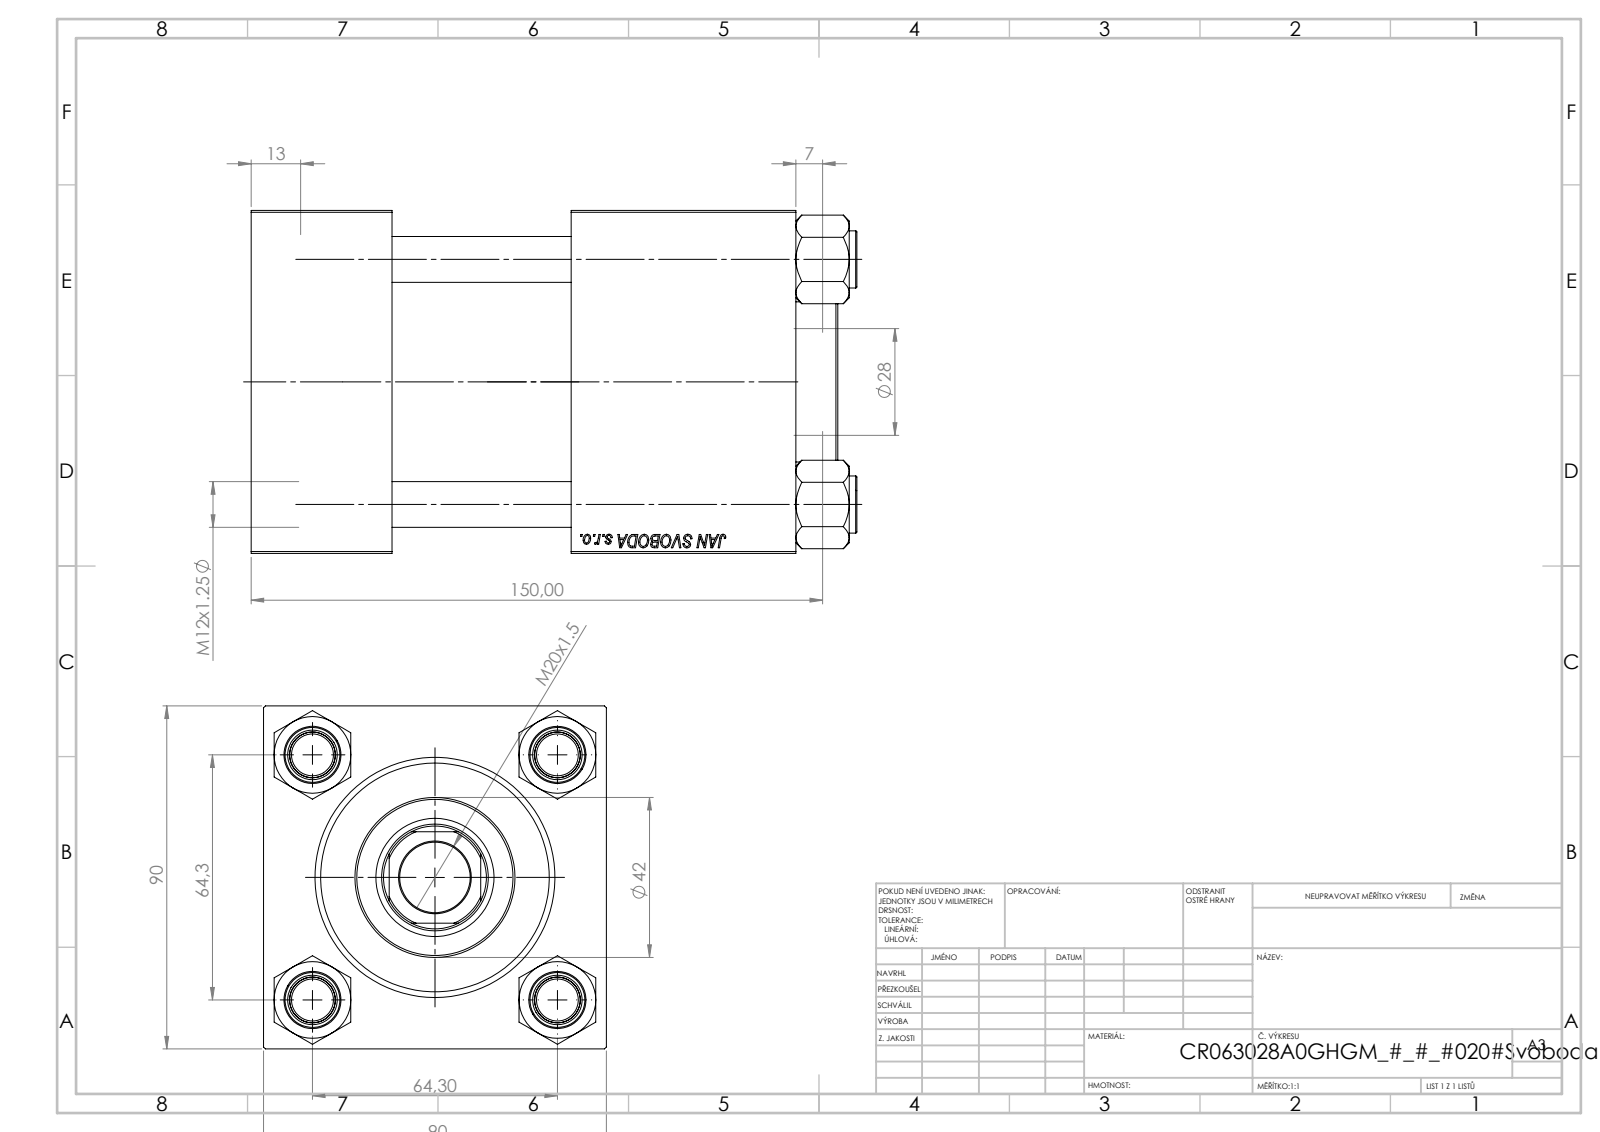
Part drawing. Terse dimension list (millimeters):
name: NUT_M5; CR025_012_A_0_G_A_G_M_020_+#_##_TYCINKA; V215_VC_A; V215CR_BODY_A (+1 more)
written by: SolidWorks 2019 (CONFIG_CONTROL_DESIGN)
unit: mm
bodies: 11 solids, 1134 faces (520 planar, 78 cylindrical, 536 other)
size: 159 × 90 × 90
volume: 888 902 mm³; area: 175 007 mm²
holes: 4× ⌀12, 2× ⌀7, 2× ⌀20.96, 2× ⌀30, 1× ⌀18.5, 1× ⌀28, 1× ⌀31, 1× ⌀50, 1× ⌀60, 1× ⌀63
bosses: 4× ⌀15, 1× ⌀69, 1× ⌀42
rounds: 1× R13.5
face distances: 90, 37, 143, 106, 59, 84, 47, 114.3, 77.3, 30.3
hole spacings: 45.47, 64.3, 90.93, 85.5
